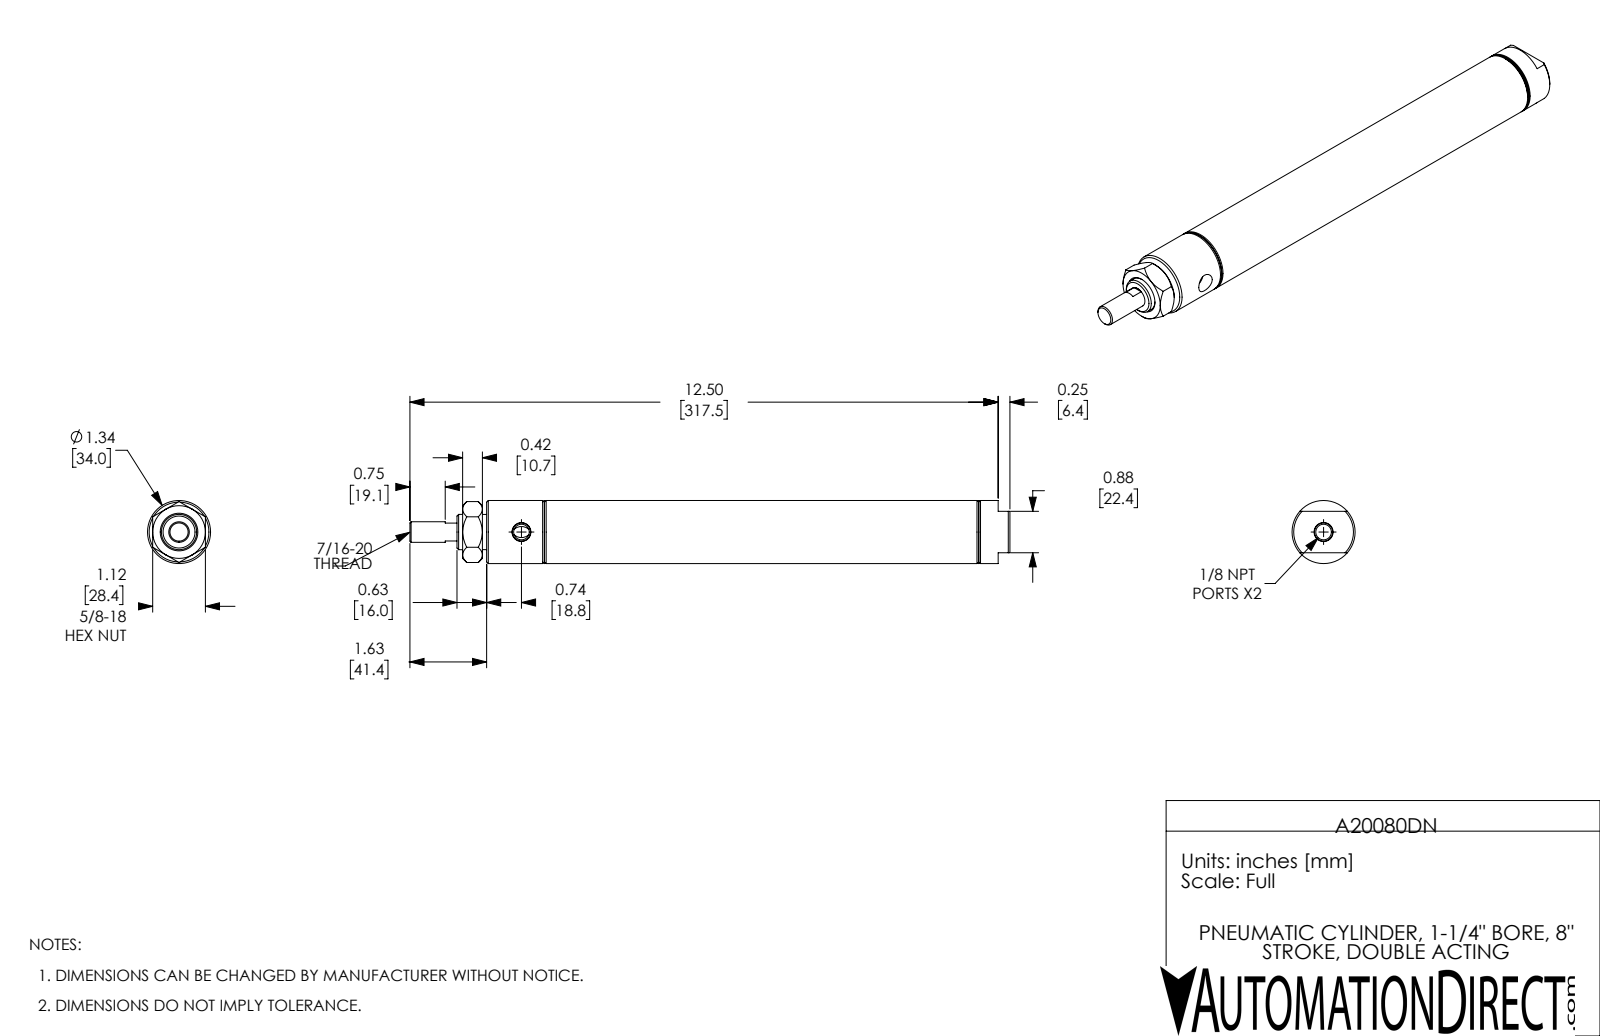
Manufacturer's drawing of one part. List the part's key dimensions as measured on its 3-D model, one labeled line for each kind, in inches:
Part name (STEP PRODUCT): A20080DN; A20080DN_Mounting Nut_D-3556; A20080DN-Rod; A20080DN-MainBody
STEP written by: SolidWorks 2017 (AUTOMOTIVE_DESIGN)
Units: inches
Bodies: 3 solids, 100 faces (33 planar, 28 cylindrical, 39 other)
Overall size (bounding box): 12.75 × 1.34 × 1.34
Volume: 7.485 in³ · Surface area: 114.6 in²
Round holes (diameter × count): ⌀0.332 ×2, ⌀0.437 ×1, ⌀0.75 ×1, ⌀1.25 ×1
Round bosses / shafts (diameter × count): ⌀1.34 ×1, ⌀0.747 ×1
Main face-to-face distances: 8.5, 0.5, 8, 1.31, 1.81, 9.81, 11.12, 9.81, 9.31, 1.31
